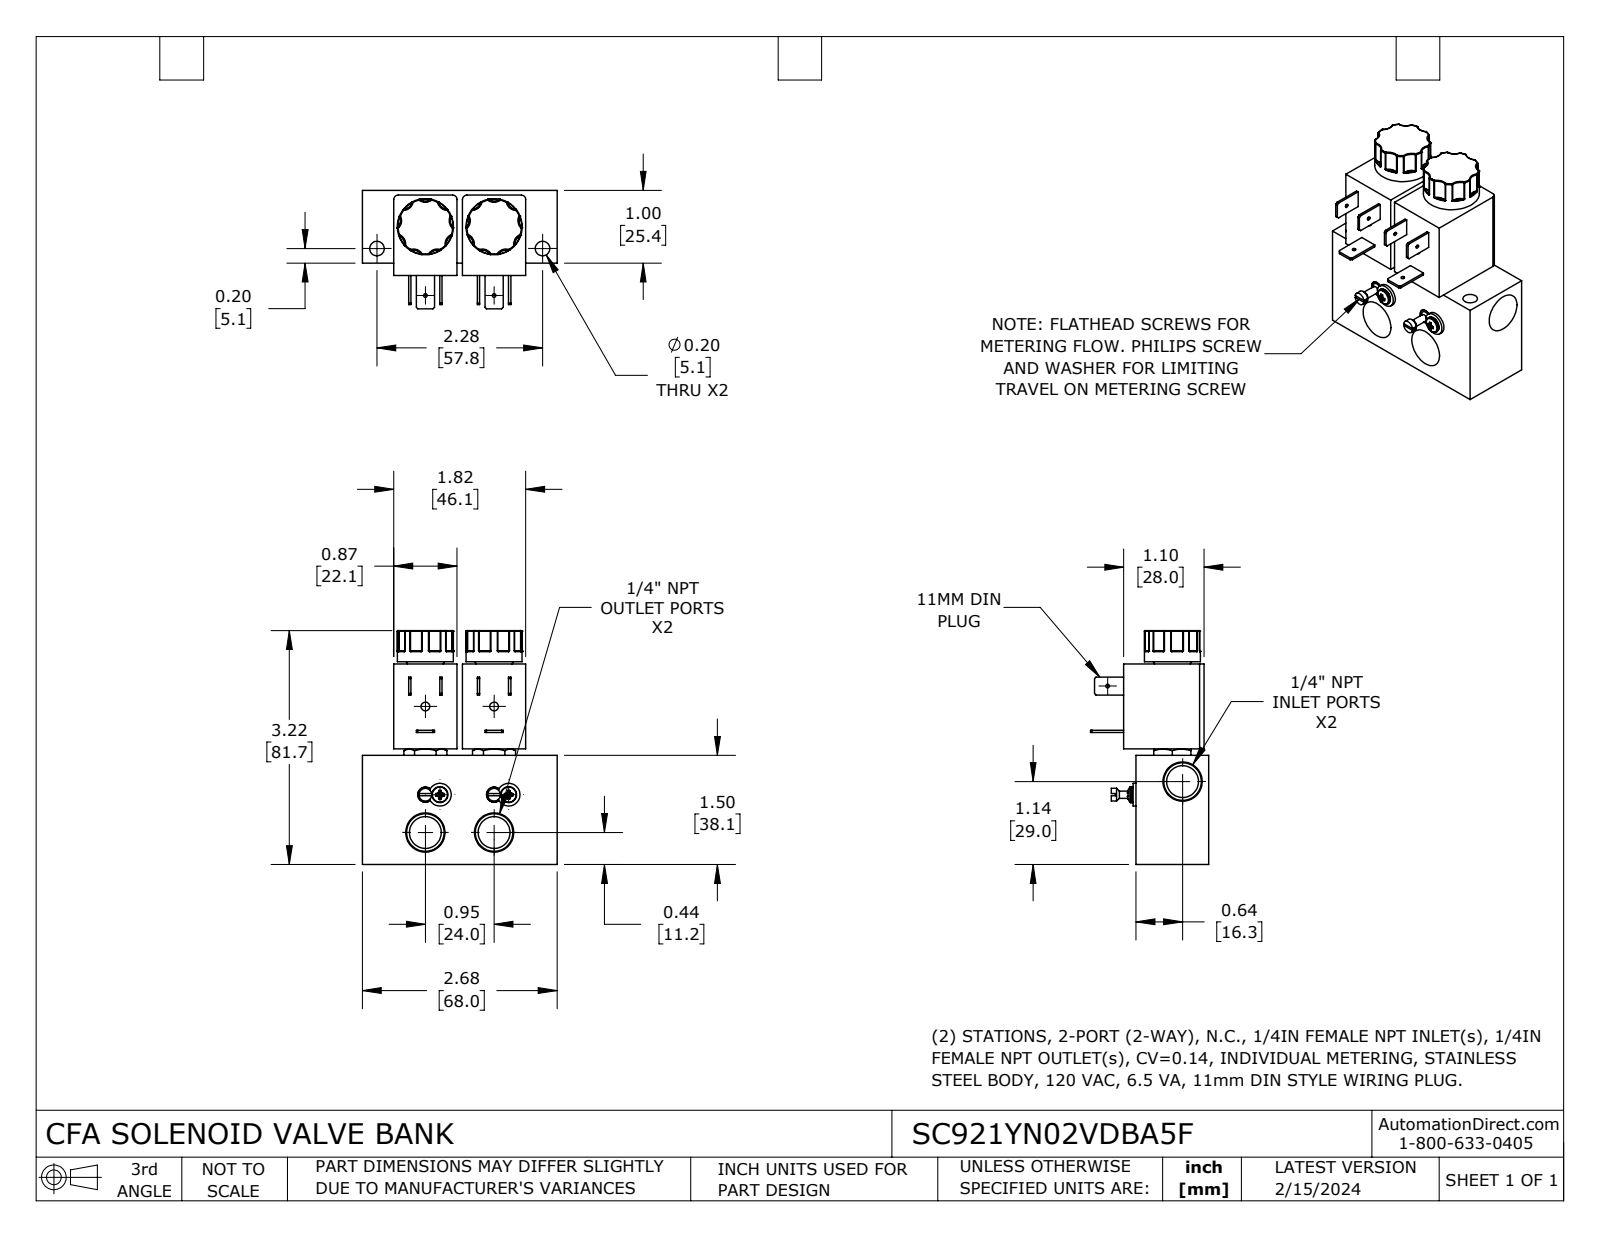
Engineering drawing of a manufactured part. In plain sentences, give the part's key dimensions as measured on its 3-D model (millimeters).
The part is named "SC921YN02VDBA5F". Its 3-D file was written by "SolidWorks 2023 (CONFIG_CONTROL_DESIGN)". It is 1 solid with 589 faces: 156 planar, 152 cylindrical and 281 other. Overall it measures 81.7 by 68 by 41.3 millimeters. Its volume is 100 900 cubic millimeters and its surface area 25 980 square millimeters. Round holes: 3 of diameter 1.3, 3 of diameter 11.1, 2 of diameter 3, 2 of diameter 5.1, 2 of diameter 5.3. Round bosses or shafts: 2 of diameter 19.6, 2 of diameter 7.9, 2 of diameter 5.6, 2 of diameter 5.2, 2 of diameter 4.4, 2 of diameter 2.6, 2 of diameter 2.5. Partial cylindrical surfaces (rounded edges, fillets, slot ends): 36 of radius 0.3, 18 of radius 3.4, 4 of radius 1.5, 1 of radius 7.8. The main face-to-face distances are 25.4, 24, 10.9, 33, 35, 57, 22.1, 38.1, 29.7, 4.3. The hole center spacings are 24, 13.2, 23.6, 27.4, 30.8, 39, 44, 44.1.
